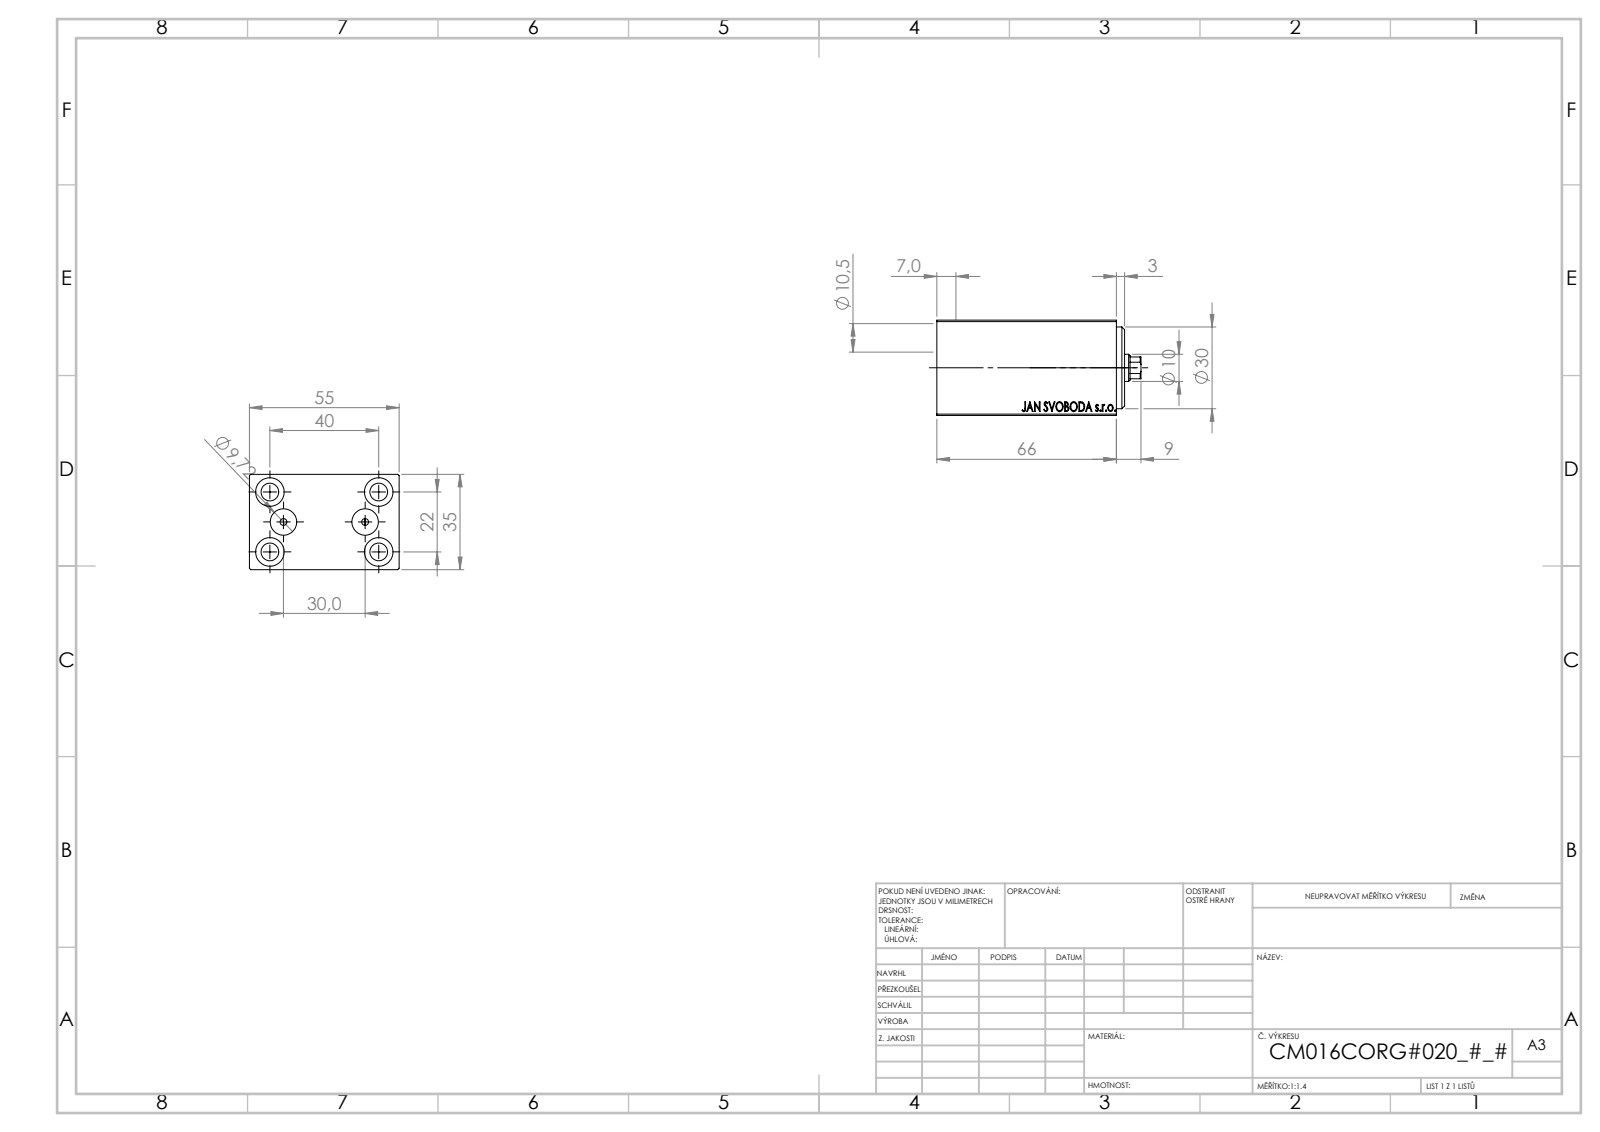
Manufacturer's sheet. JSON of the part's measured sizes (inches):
{"part_name": "V450CM_VC_B; V450CM_C_Body; V450CM_C_VCP", "step_written_by": "SolidWorks 2019 (CONFIG_CONTROL_DESIGN)", "units": "inches", "bodies": {"solids": 3, "faces": 861, "planar": 409, "cylindrical": 58, "other": 394}, "overall_size": [2.953, 2.165, 1.378], "volume_in3": 6.891, "surface_area_in2": 46.99, "round_holes": [[0.256, 4], [0.413, 4], [0.098, 2], [0.383, 2], [0.177, 1], [0.394, 1], [0.531, 1], [0.571, 1], [0.63, 1], [0.709, 1], [1.181, 1]], "partial_cylinders_radius": [[0.177, 1]], "face_to_face_distances": [1.378, 2.165, 0.197, 2.402, 0.118, 2.598, 0.394, 2.323, 0.315, 2.717], "hole_center_spacings": [0.476, 0.899, 1.444, 0.591, 0.866, 1.575, 1.797, 1.181]}
